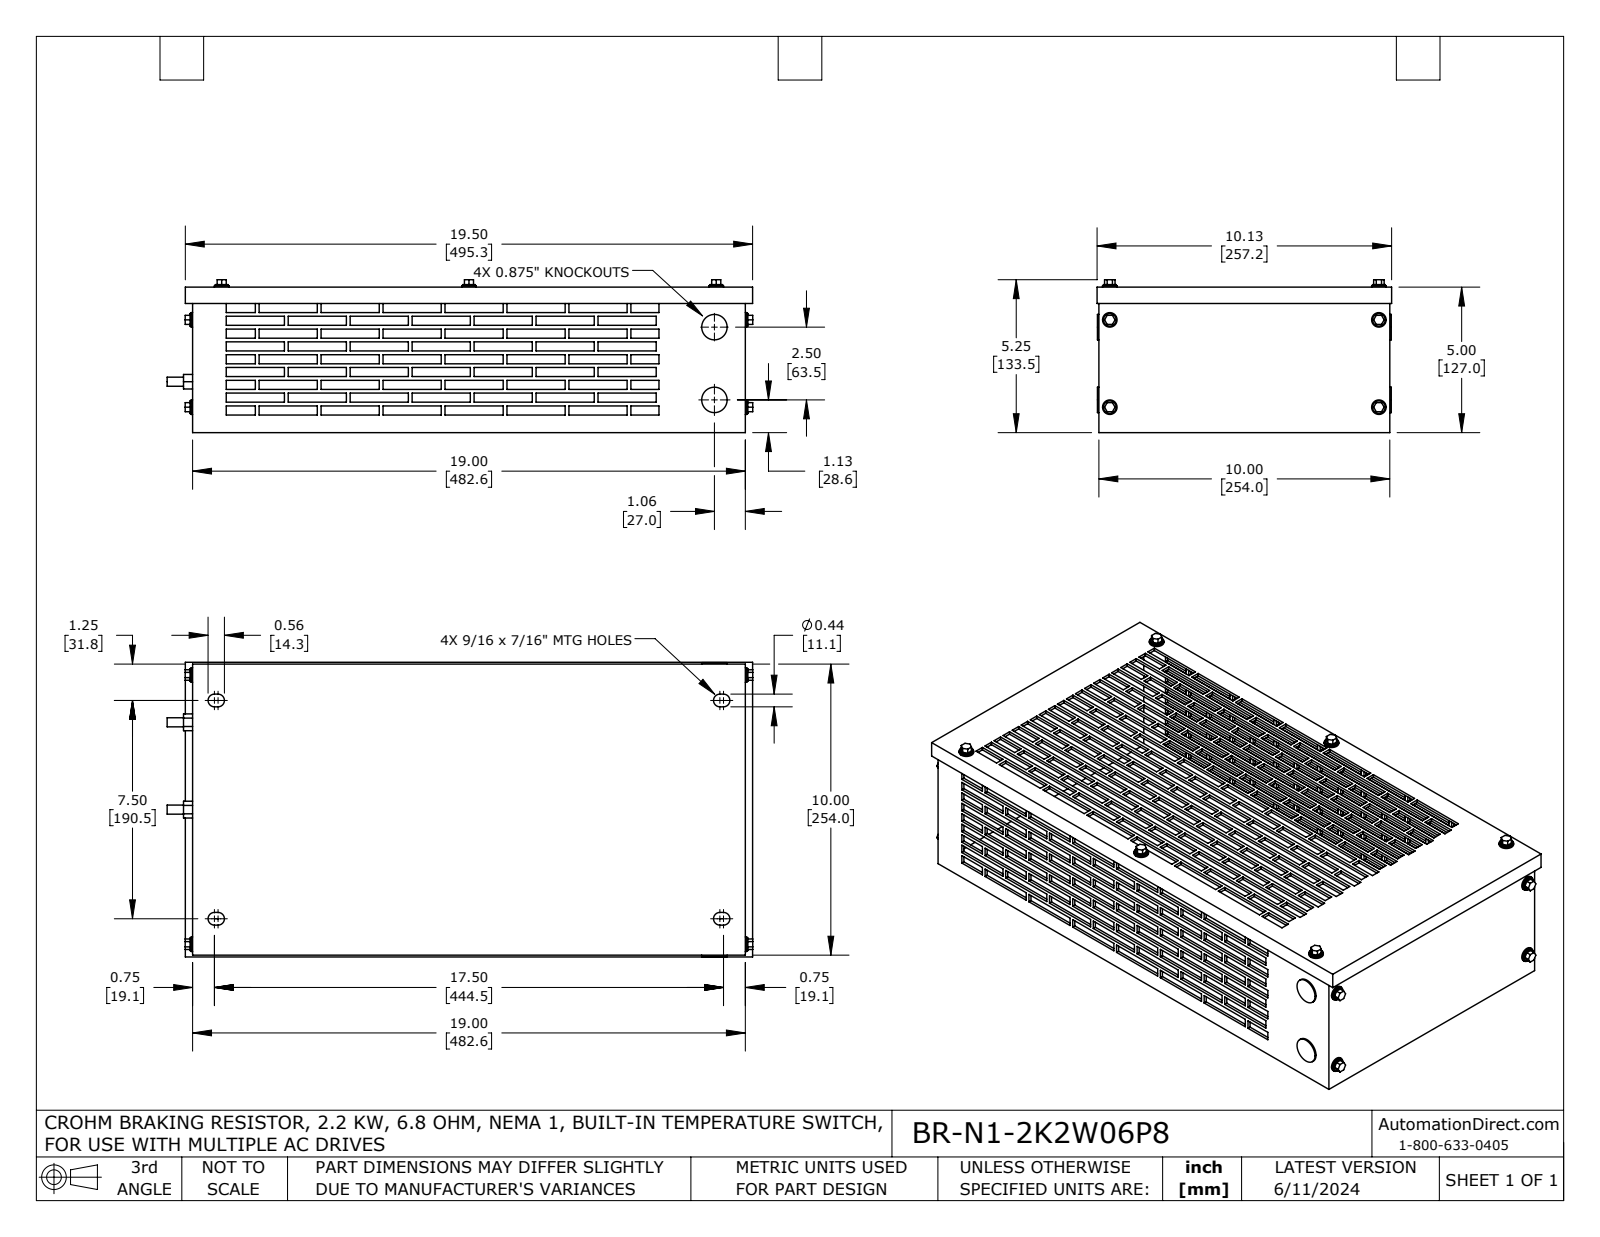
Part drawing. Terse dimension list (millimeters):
name: BR-N1-2K2W06P8
written by: SolidWorks 2021 (AUTOMOTIVE_DESIGN)
unit: mm
bodies: 35 solids, 1454 faces (1342 planar, 112 cylindrical, 0 other)
size: 511.3 × 257.2 × 133.5
volume: 836 900 mm³; area: 745 200 mm²
holes: 10× ⌀6.4, 2× ⌀19.1
bosses: 10× ⌀12.7, 10× ⌀11.1, 2× ⌀22.2, 2× ⌀8
rounds: 8× R5.6
face distances: 2.5, 124.5, 127, 121.9, 480.1, 251.5, 254, 482.6, 477.5, 248.9
hole spacings: 235, 215.9, 319.1, 76.2, 247, 431.8, 491.6, 63.5
